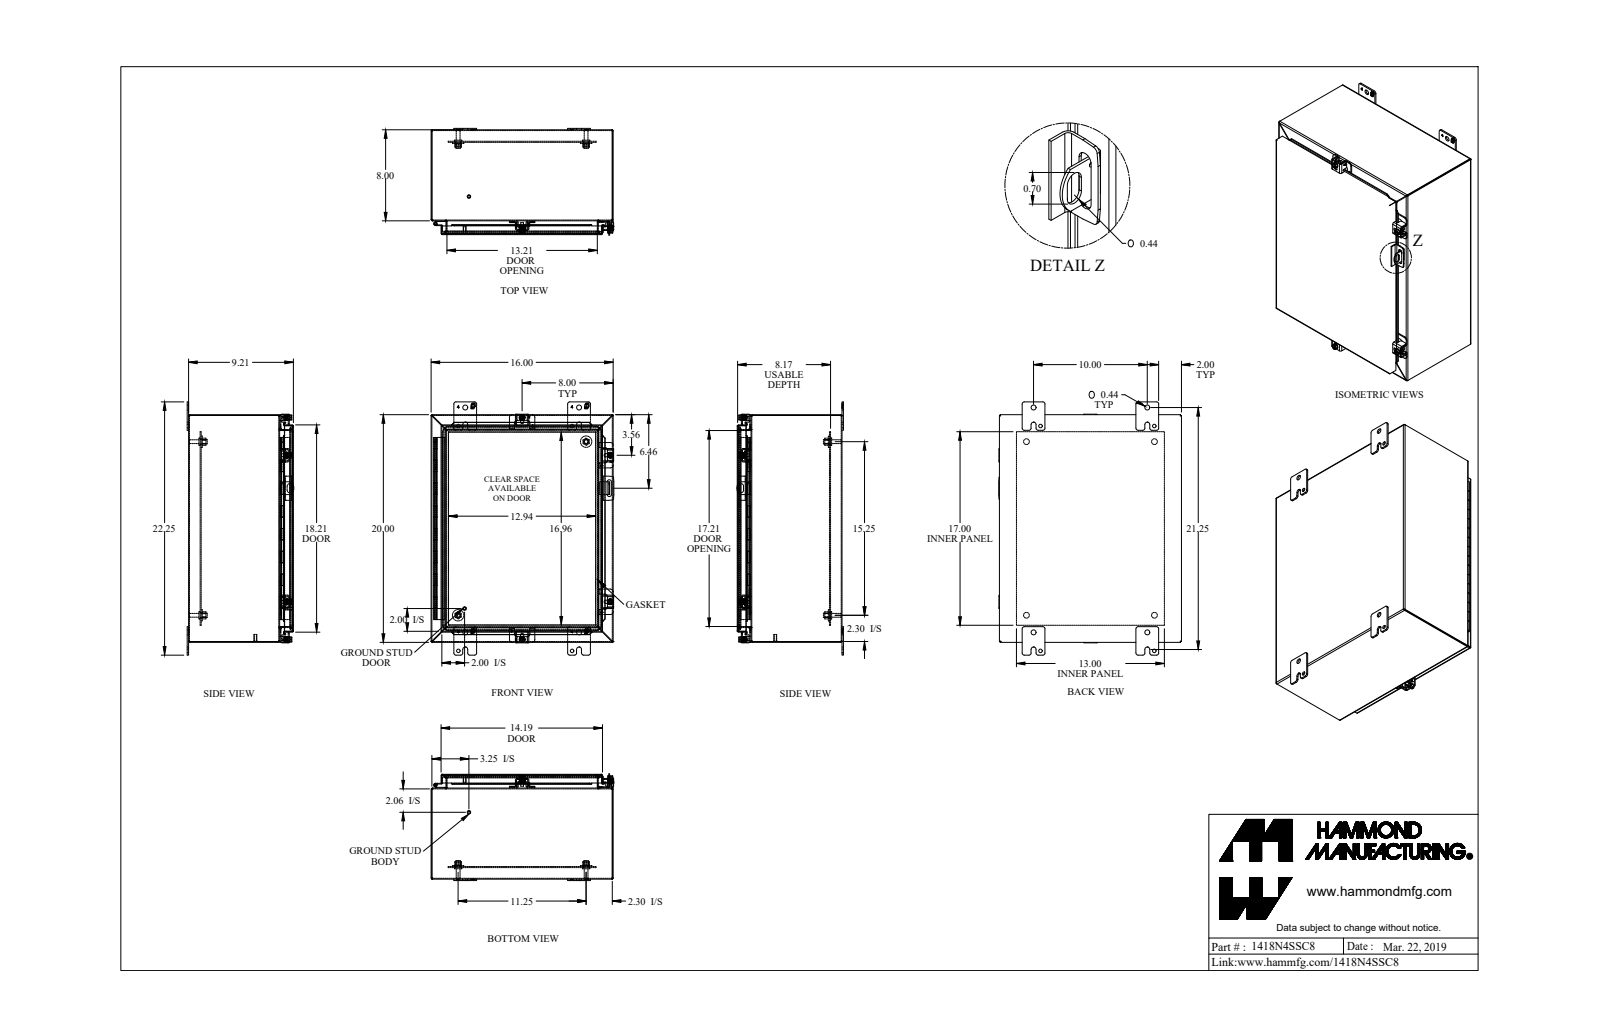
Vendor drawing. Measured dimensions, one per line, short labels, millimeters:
name: 1418N4SSC8_Default
written by: SolidWorks 2019 (CONFIG_CONTROL_DESIGN)
unit: mm
bodies: 39 solids, 1454 faces (905 planar, 457 cylindrical, 92 other)
size: 565.2 × 408 × 238.1
volume: 2 166 000 mm³; area: 2 266 000 mm²
holes: 4× ⌀5.4, 4× ⌀6.7, 4× ⌀8, 4× ⌀9.5, 4× ⌀11.1, 4× ⌀12.7, 2× ⌀7.8, 2× ⌀11.3, 1× ⌀3.2, 1× ⌀4.7
bosses: 4× ⌀16.5, 4× ⌀12.7, 4× ⌀9.9, 4× ⌀9.5, 4× ⌀8.4, 4× ⌀6.2, 2× ⌀25.4, 2× ⌀8
rounds: 26× R4.8, 24× R0.9, 24× R2.7, 21× R1.2, 21× R3.6, 20× R6.4, 8× R1.1, 8× R3.2
face distances: 1.8, 404.6, 230.3, 232.1, 1.8, 232.1, 233.9, 506.2, 23.8, 25.6
hole spacings: 463.9, 152.7, 254, 61.8, 77.9, 280.4, 285.8, 387.4
